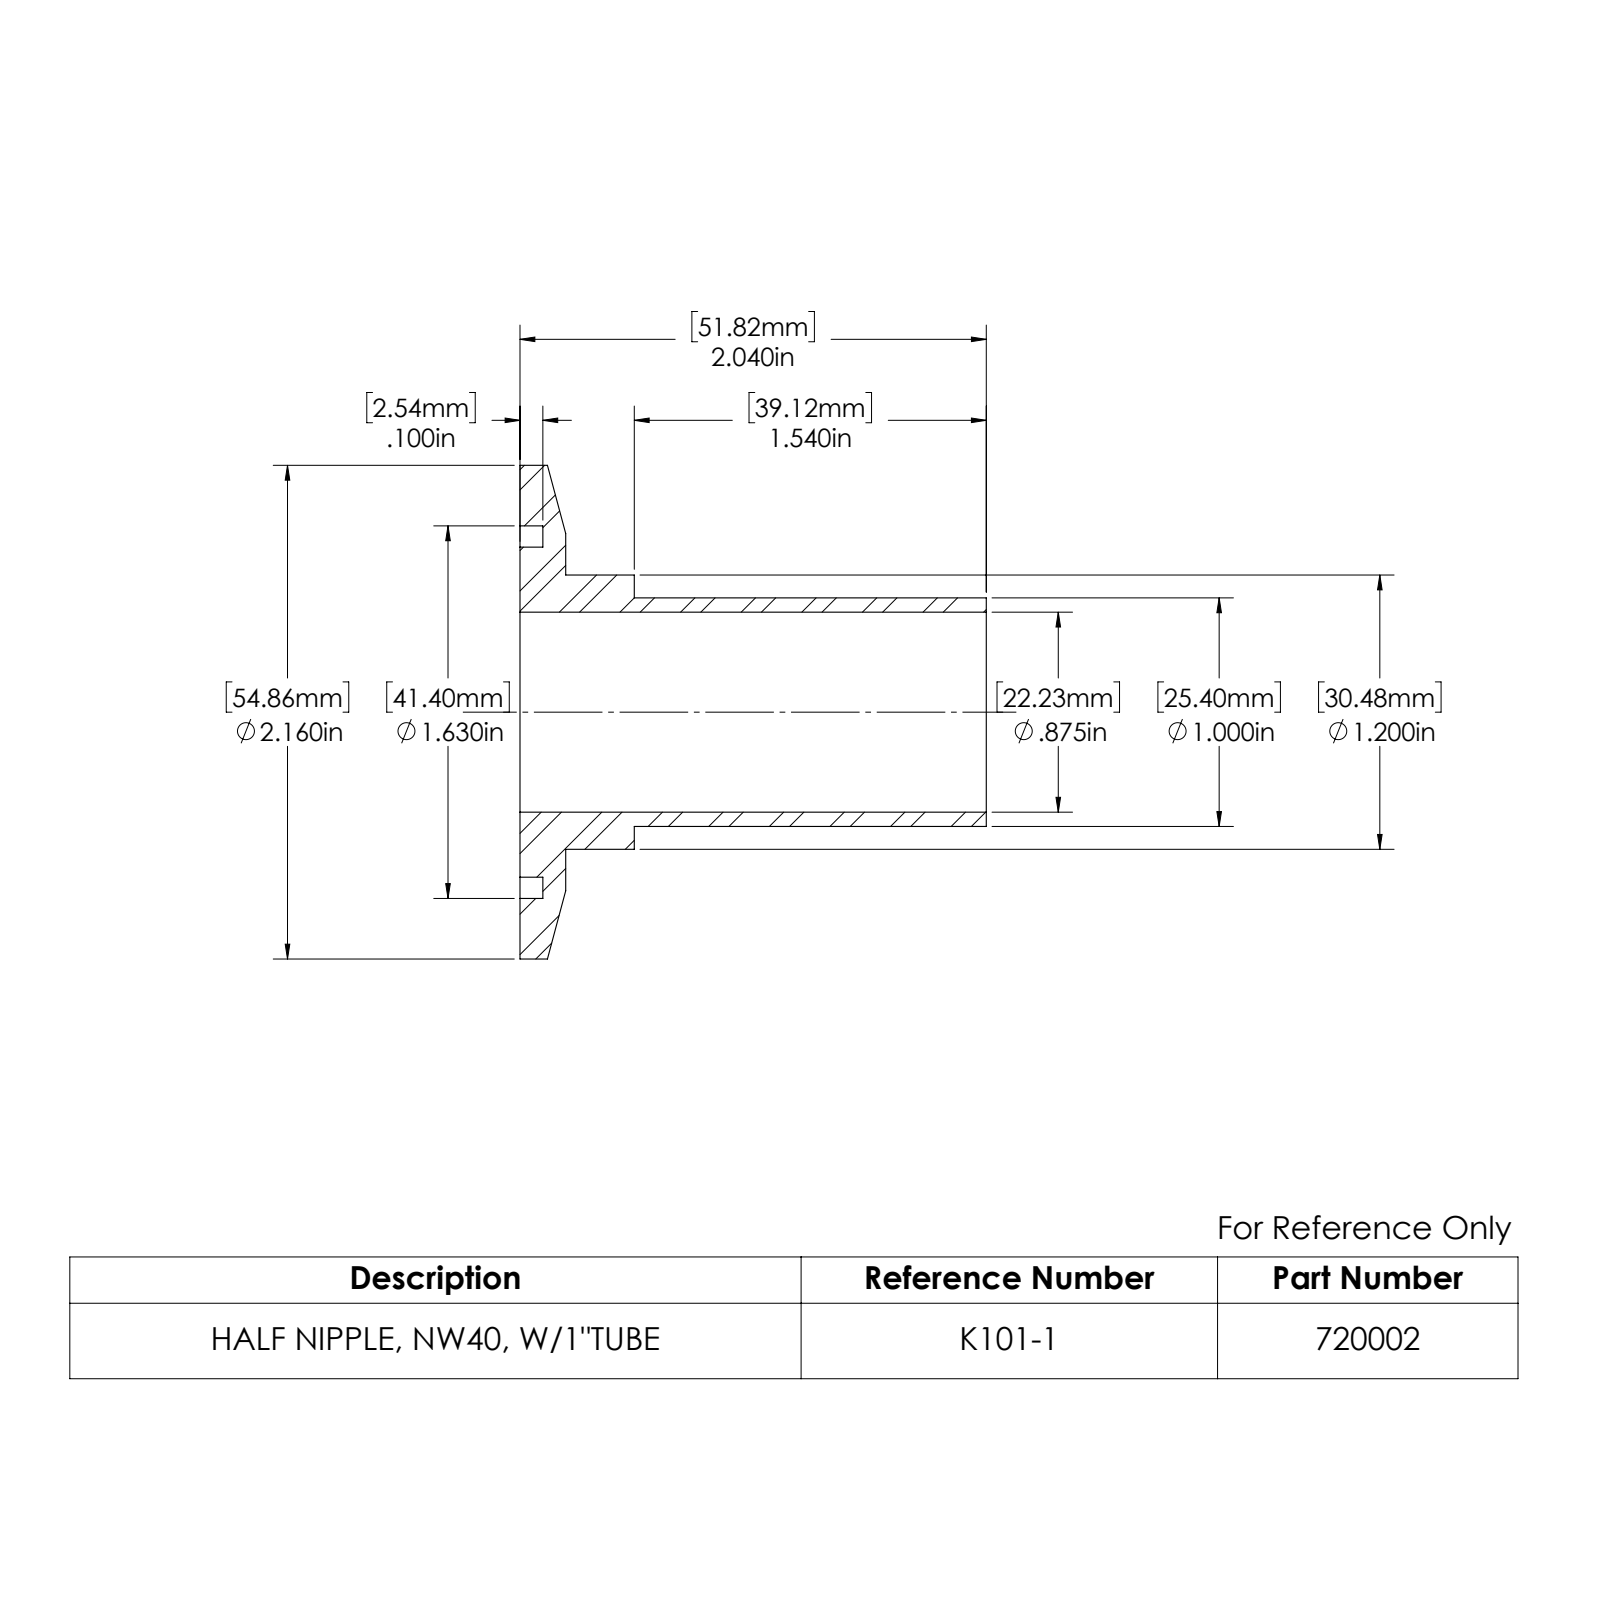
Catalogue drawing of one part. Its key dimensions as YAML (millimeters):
part_name: "720002"
step_written_by: "SolidWorks 2022 (AUTOMOTIVE_DESIGN)"
units: millimeters
bodies: {solids: 1, faces: 20, planar: 6, cylindrical: 12, other: 2}
overall_size: [54.9, 54.9, 51.8]
volume: 15400
surface_area: 12610
round_holes:
  - {diameter: 22.2, count: 1}
  - {diameter: 41.4, count: 1}
round_bosses_or_shafts:
  - {diameter: 54.9, count: 1}
  - {diameter: 36.7, count: 1}
  - {diameter: 30.5, count: 1}
  - {diameter: 25.4, count: 1}
face_to_face_distances: [2.5, 5.1, 7.6, 10.2, 12.7, 39.1, 46.7, 49.3, 51.8]
